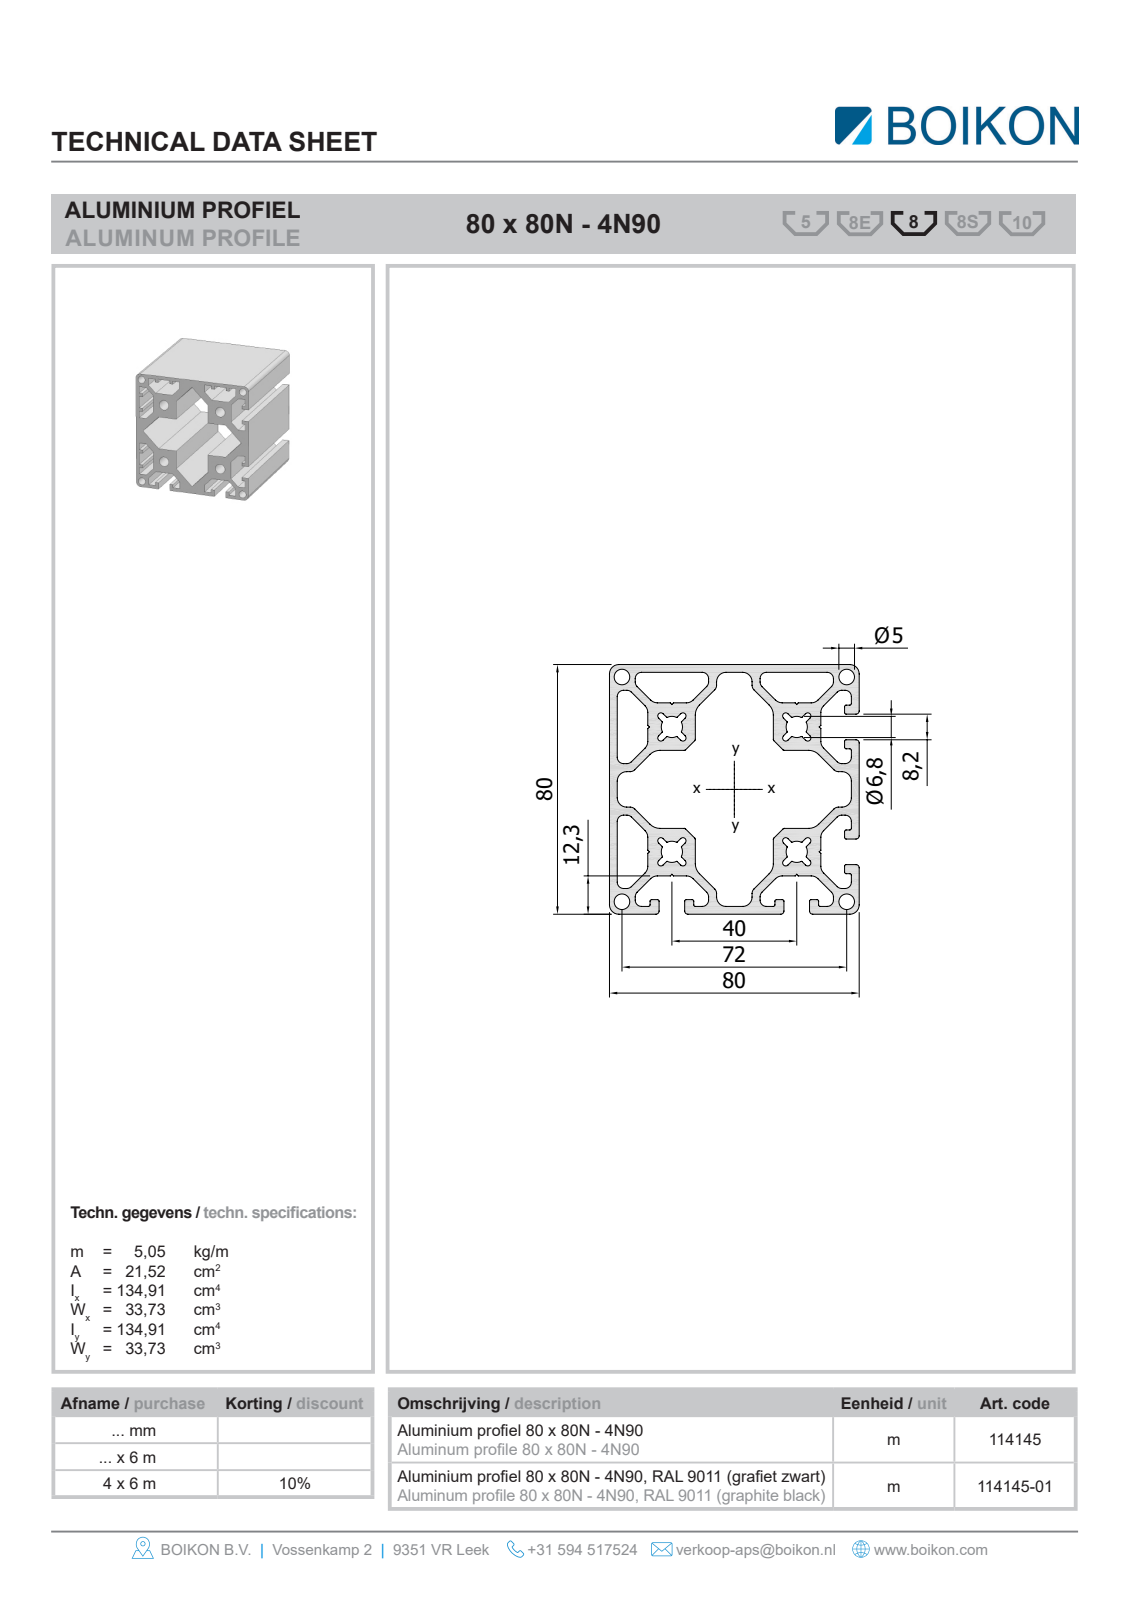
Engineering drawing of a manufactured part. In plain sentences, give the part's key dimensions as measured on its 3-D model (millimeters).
The part is named "Root; 11414580x80L-4N90BOIKON0". Its 3-D file was written by "HiCAD 2013 1802.4 Build 509 (AUTOMOTIVE_DESIGN)". It is 1 solid with 146 faces: 134 planar, 12 cylindrical and 0 other. Overall it measures 1000 by 80 by 80 millimeters. Its volume is 1 958 000 cubic millimeters and its surface area 1 232 000 square millimeters. Round holes: 4 of diameter 5, 4 of diameter 6.8. Partial cylindrical surfaces (rounded edges, fillets, slot ends): 4 of radius 3. The main face-to-face distances are 40, 1.8, 80, 27.7, 52.3, 28.28, 12.3, 67.7, 15.4, 4.5. The hole center spacings are 58.24, 22.63, 40, 72, 79.2, 56.57, 101.82.
